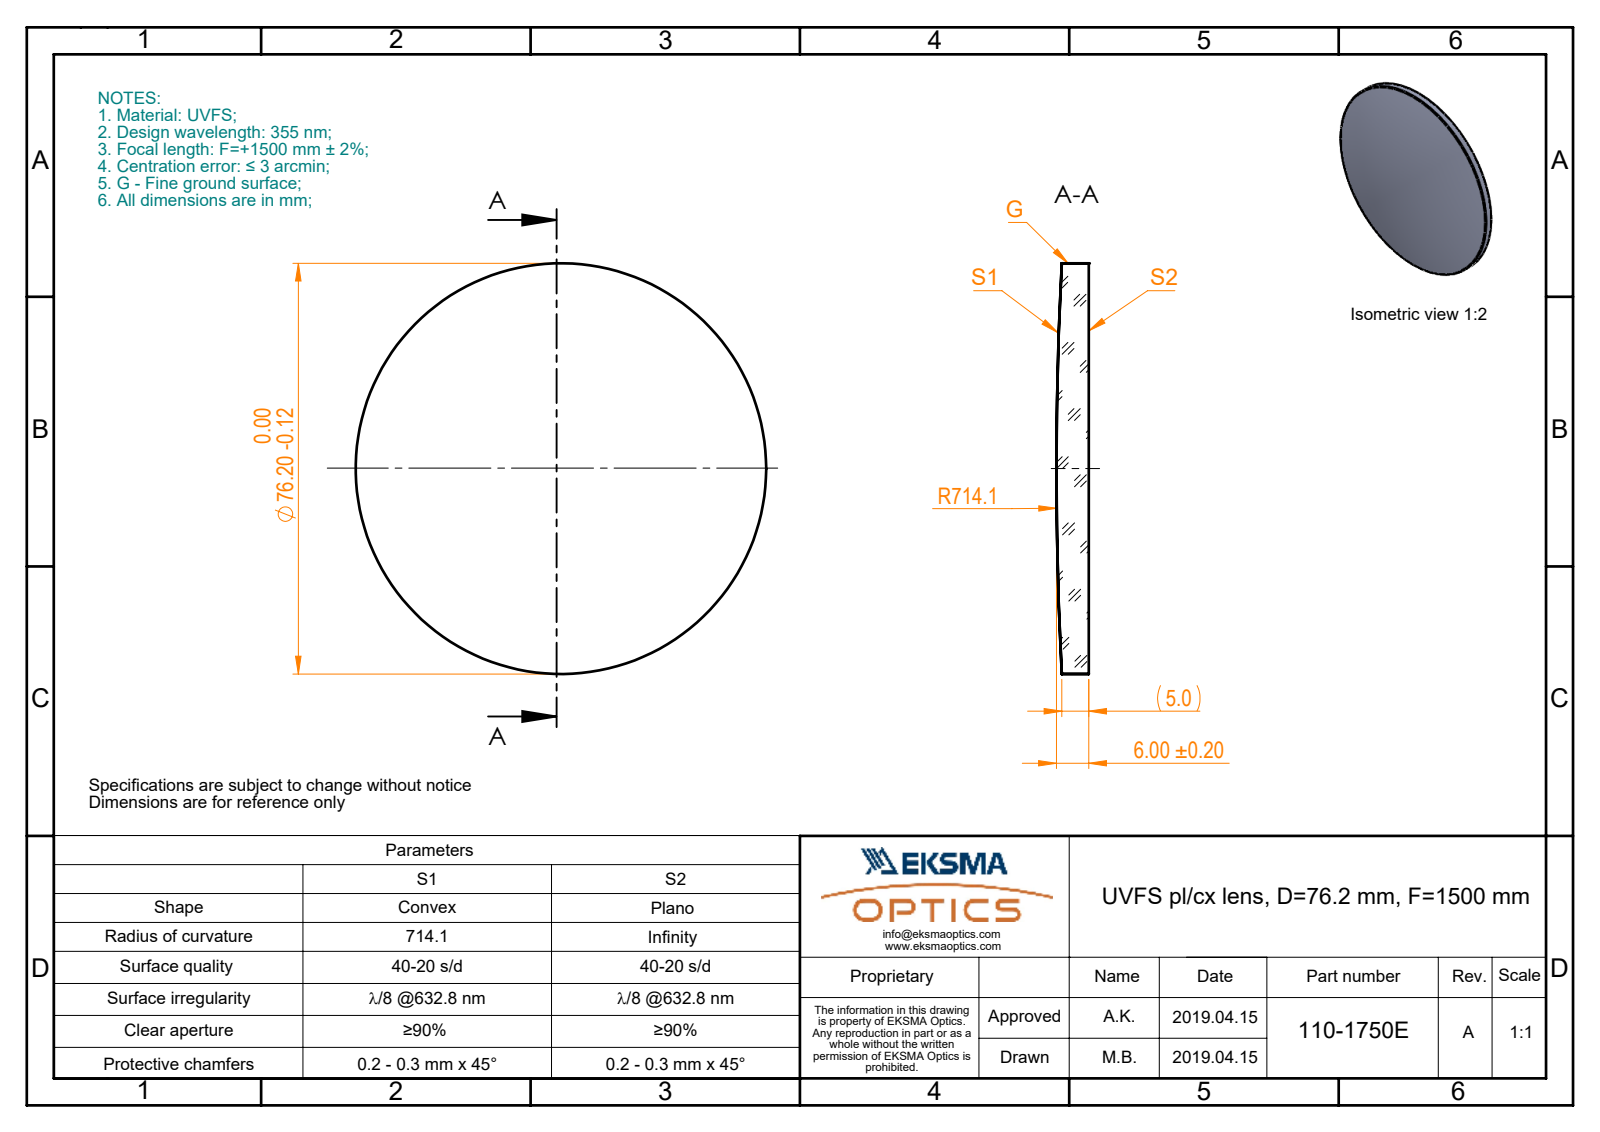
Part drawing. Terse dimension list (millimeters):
name: 110-1750E UVFS pl-cx 76.2 F1500
written by: SolidWorks 2017 (CONFIG_CONTROL_DESIGN)
unit: mm
bodies: 1 solid, 5 faces (1 planar, 2 cylindrical, 2 other)
size: 76.2 × 76.2 × 6
volume: 25 044 mm³; area: 10 317 mm²
bosses: 1× ⌀76.2
